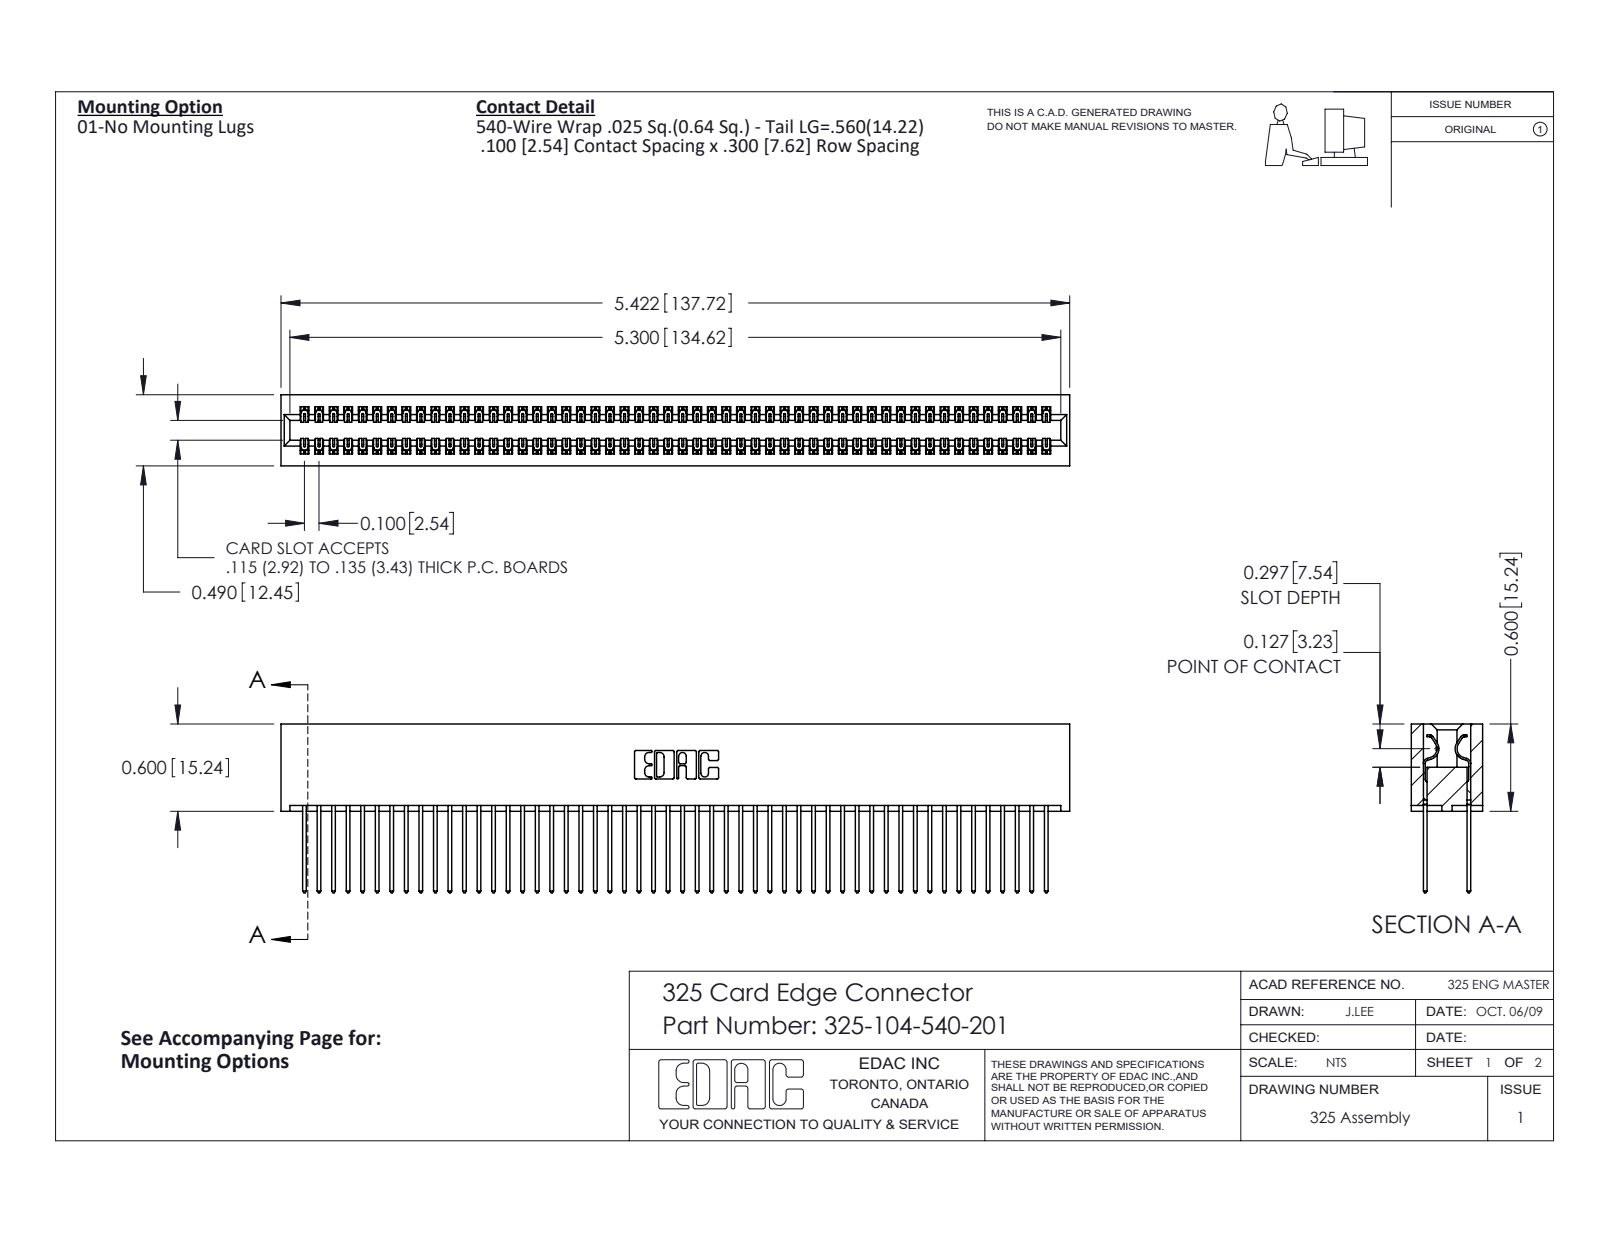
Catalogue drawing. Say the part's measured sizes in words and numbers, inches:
The part is named "325-292-001_325-293-140; 325-104-540-201; 325 Part_Lugless". Its 3-D file was written by "SolidWorks 2016 (CONFIG_CONTROL_DESIGN)". It is 105 solids with 5514 faces: 3810 planar, 1704 cylindrical and 0 other. Overall it measures 5.422 by 1.16 by 0.49 inches. Its volume is 1.151 cubic inches and its surface area 39.7 square inches. Partial cylindrical surfaces (rounded edges, fillets, slot ends): 156 of radius 0.006, 104 of radius 0.01, 22 of radius 0.01, 6 of radius 0.007, 6 of radius 0.031, 3 of radius 0.026, 2 of radius 0.014, 2 of radius 0.022. The main face-to-face distances are 0.083, 0.407, 0.3, 0.107, 0.383, 0.025, 0.325, 0.49, 0.275, 0.56.
